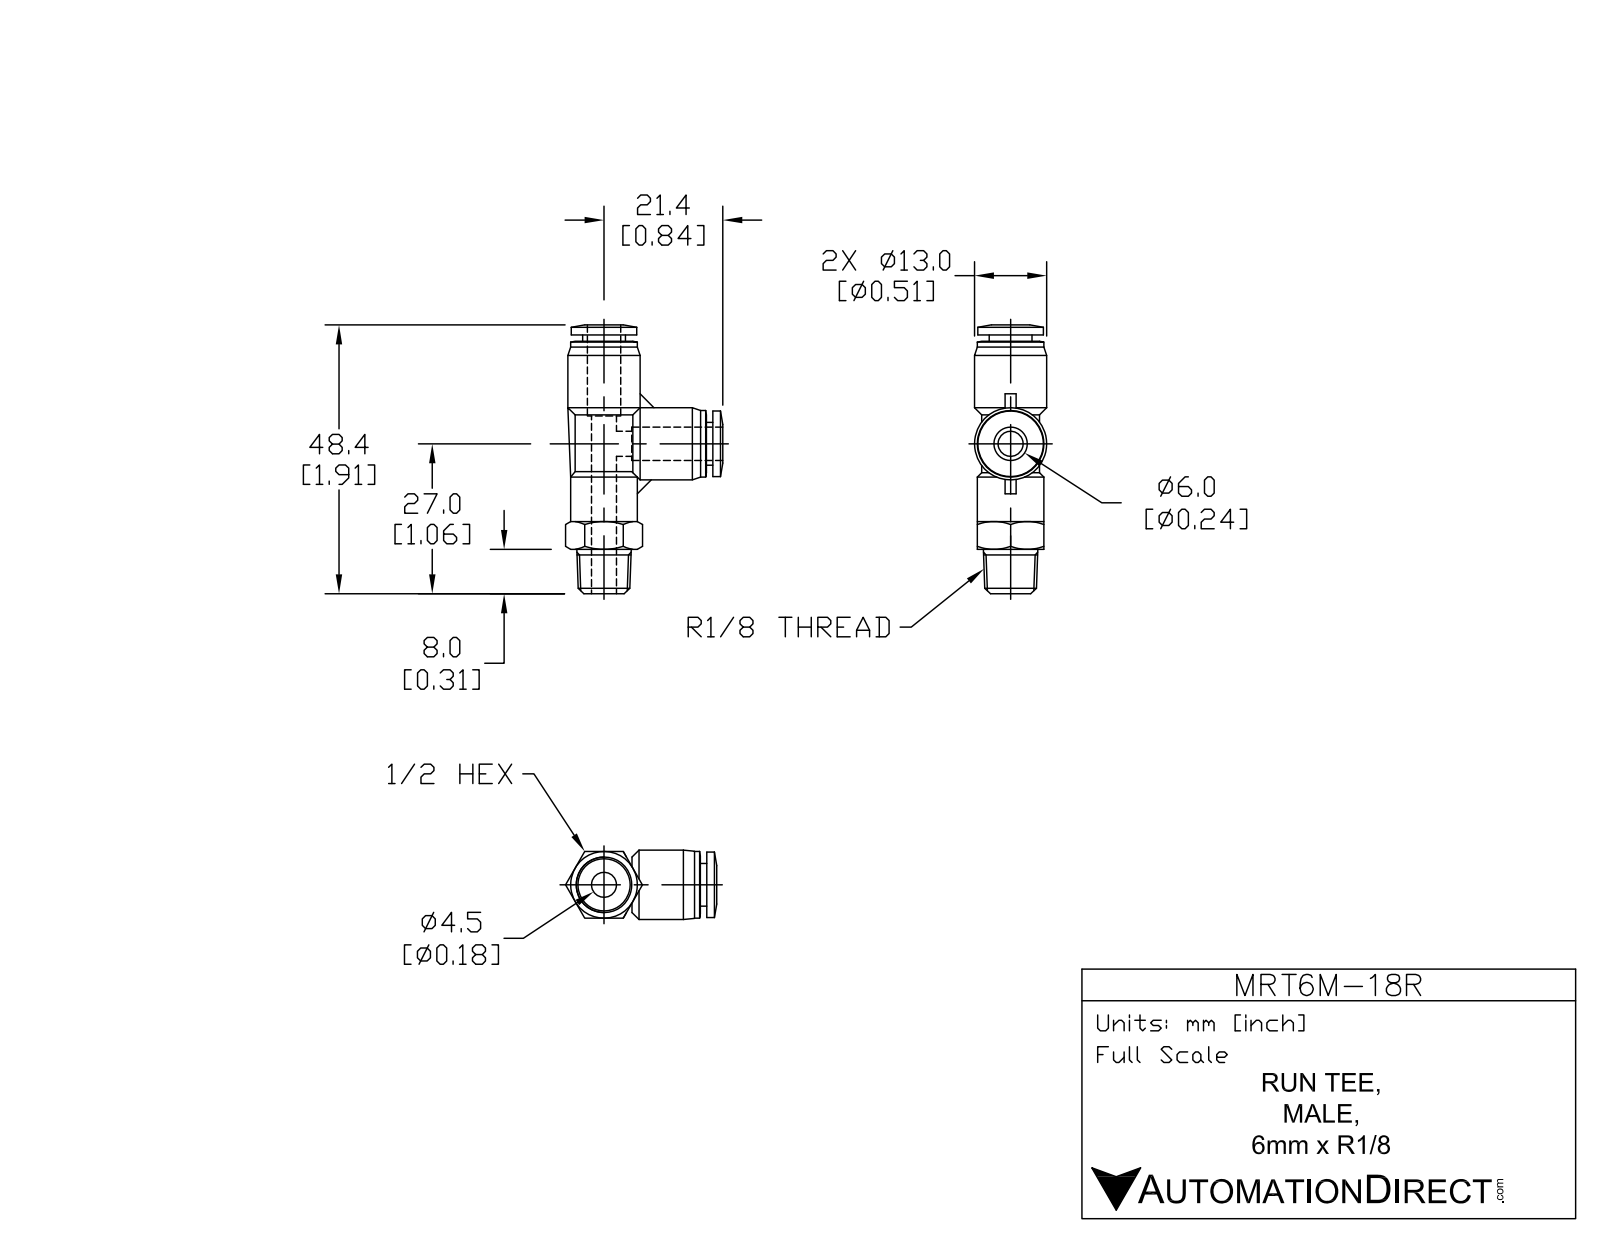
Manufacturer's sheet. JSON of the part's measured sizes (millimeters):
{"part_name": "MRT6M-18R", "step_written_by": "SolidWorks 2015 (AUTOMOTIVE_DESIGN)", "units": "millimeters", "bodies": {"solids": 1, "faces": 97, "planar": 24, "cylindrical": 31, "other": 42}, "overall_size": [48.4, 28.3, 13], "volume_mm3": 5540, "surface_area_mm2": 3979, "round_holes": [[4, 2], [6.3, 2]], "round_bosses_or_shafts": [[13, 2], [12, 2], [11.8, 2], [10.4, 2], [7.7, 2]], "face_to_face_distances": [12, 1.1, 5, 7, 37.4, 38.6, 13.5, 14.6, 8, 45.4]}
